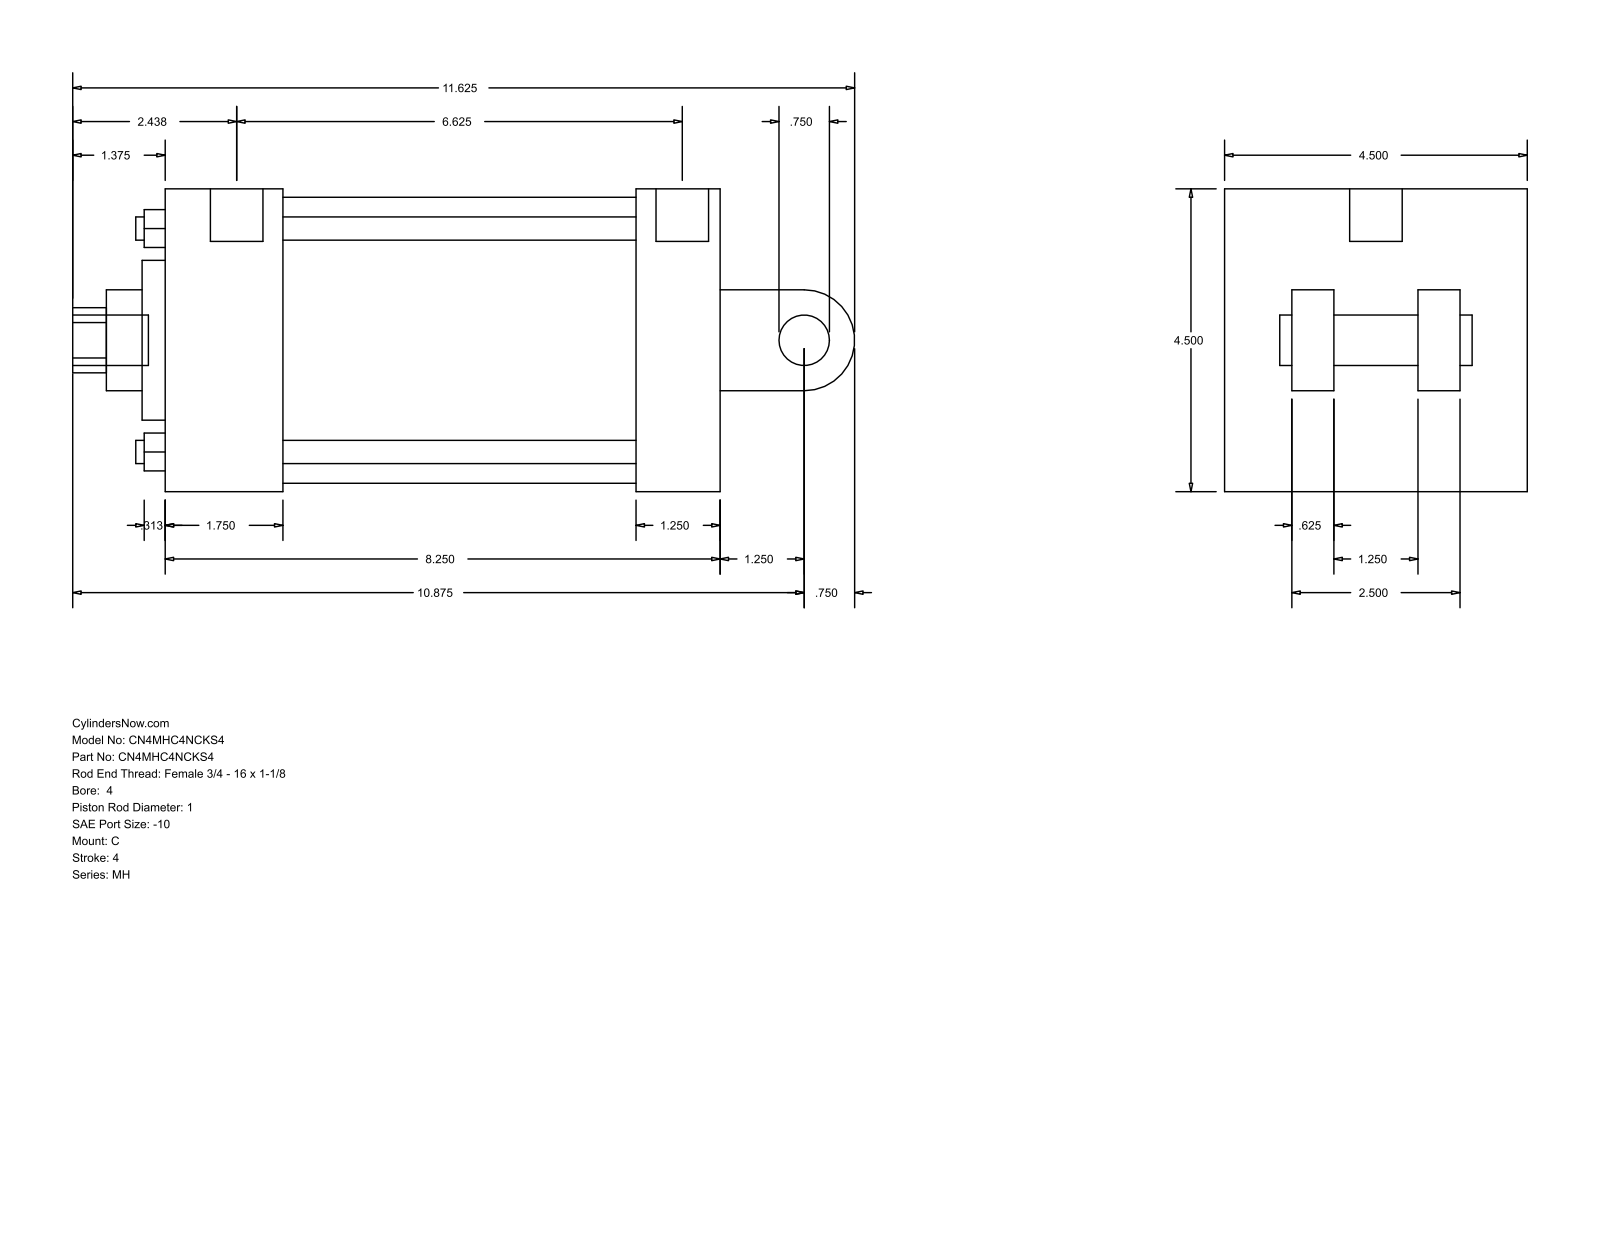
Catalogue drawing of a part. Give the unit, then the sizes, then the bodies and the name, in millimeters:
Units: millimetres
Overall size (bounding box): 295.27 × 114.3 × 114.3
Round holes (diameter × count): ⌀8.76 ×4, ⌀8.73 ×2, ⌀19.84 ×1, ⌀25.4 ×1, ⌀38.1 ×1, ⌀60.33 ×1, ⌀107.95 ×1
Round bosses / shafts (diameter × count): ⌀19.05 ×2, ⌀8.73 ×2, ⌀19.84 ×1
Partial cylindrical surfaces — rounded edges, fillets, slot ends (radius × count): R12.29 ×1, R19.05 ×1
Main face-to-face distances: 114.3, 209.55, 44.46, 177.8, 133.34, 165.09, 31.75, 73.03, 15.87, 47.63
Hole centre spacings: 59.62, 84.32, 119.25, 1.59
Bodies: 0 solids, 101 faces (71 planar, 30 cylindrical, 0 other)
Part name (STEP PRODUCT): MH_C__0400_1
STEP written by: GSSL Pune (CONFIG_CONTROL_DESIGN)
